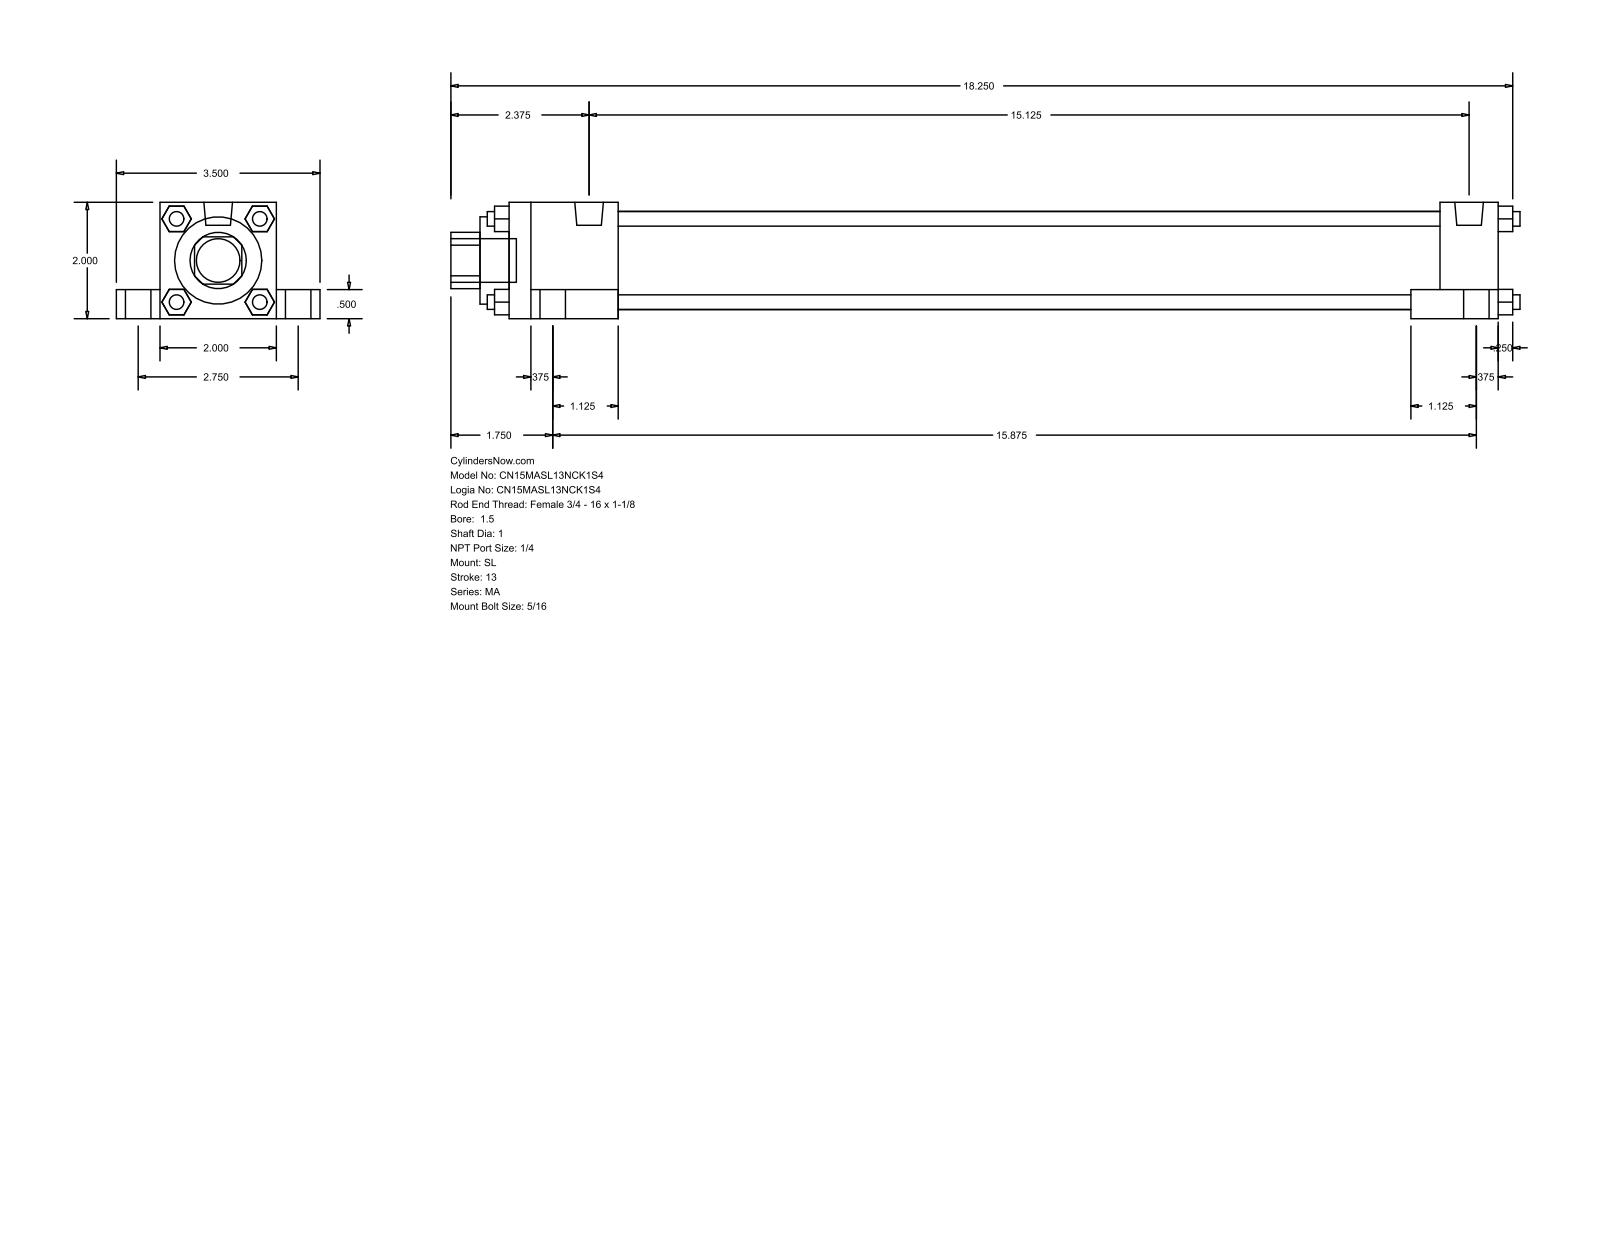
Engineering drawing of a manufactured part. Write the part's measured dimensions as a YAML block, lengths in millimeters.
part_name: "MA_SL__0150_1"
step_written_by: "GSSL Pune (CONFIG_CONTROL_DESIGN)"
units: millimeters
bodies: {solids: 0, faces: 148, planar: 112, cylindrical: 36, other: 0}
overall_size: [466.73, 88.9, 50.8]
round_holes:
  - {diameter: 25.4, count: 1}
  - {diameter: 38.1, count: 1}
  - {diameter: 42.93, count: 1}
round_bosses_or_shafts:
  - {diameter: 17.46, count: 4}
  - {diameter: 11.11, count: 4}
  - {diameter: 7.94, count: 4}
  - {diameter: 6.35, count: 4}
  - {diameter: 12.49, count: 2}
  - {diameter: 19.05, count: 1}
partial_cylinders:
  - {radius: 12.29, count: 1}
face_to_face_distances: [50.8, 12.7, 19.05, 69.85, 9.52, 38.1, 6.35, 431.8, 25.4, 406.4]
